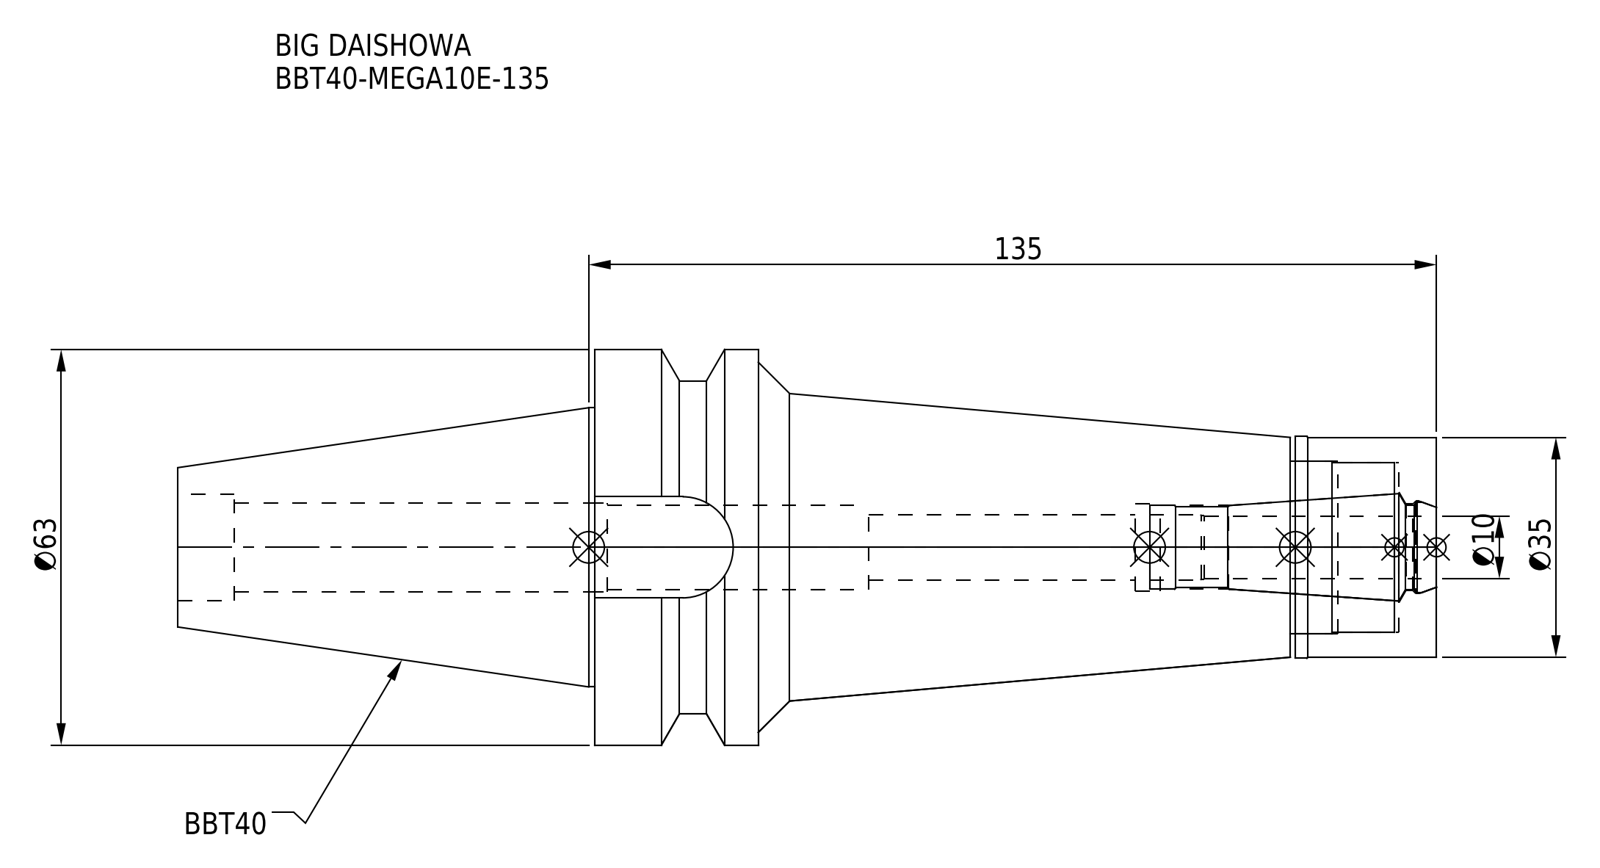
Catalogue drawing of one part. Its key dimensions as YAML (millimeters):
part_name: "BBT40-MEGA10E-135; BBT40ME10135-100_ASM.stp; DXF_TEMP_ASSY_ASM_4_ASM.stp; BBT40-MEGA10E-135-100.stp (+3 more)"
step_written_by: "SolidWorks 2019 (CONFIG_CONTROL_DESIGN)"
units: millimeters
bodies: {solids: 2, faces: 81, planar: 21, cylindrical: 40, other: 20}
overall_size: [200.4, 63, 63]
volume: 251194
surface_area: 43951
round_holes:
  - {diameter: 10.4, count: 1}
  - {diameter: 13.3, count: 1}
  - {diameter: 13.5, count: 1}
  - {diameter: 13.8, count: 1}
  - {diameter: 13.9, count: 1}
  - {diameter: 14.2, count: 1}
  - {diameter: 14.7, count: 1}
  - {diameter: 17, count: 1}
  - {diameter: 27, count: 1}
  - {diameter: 27.5, count: 1}
round_bosses_or_shafts:
  - {diameter: 63, count: 1}
  - {diameter: 53, count: 1}
  - {diameter: 44.45, count: 1}
  - {diameter: 35.3, count: 1}
  - {diameter: 35, count: 1}
partial_cylinders:
  - {radius: 8.05, count: 1}
face_to_face_distances: [134, 108, 26, 22.5, 85.5, 111.5, 23.3, 0.8, 84.7, 110.7]
